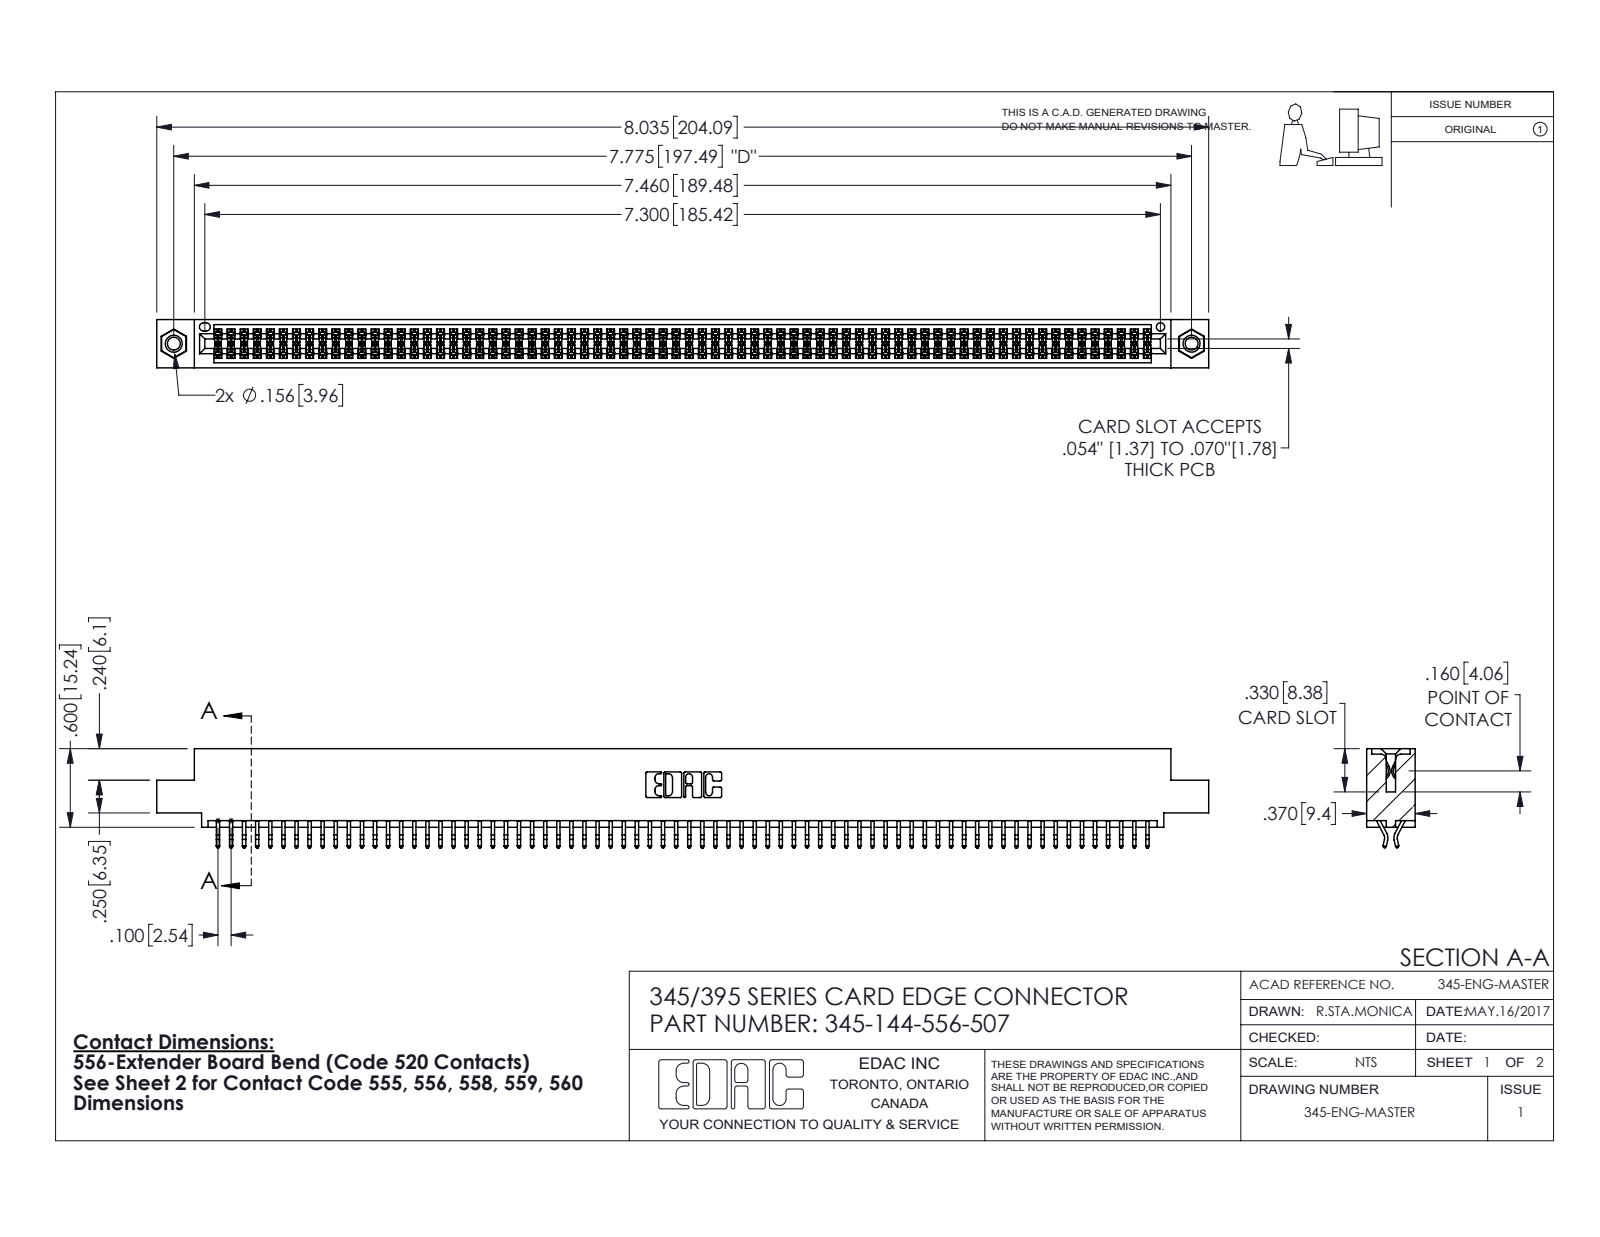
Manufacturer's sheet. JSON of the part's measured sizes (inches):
{"part_name": "345 Part_0.110 Offset - 0.156 Dia-TI; 345-292-001_556 Tail; 345-144-556-507; 345-250-001_345-250-005-103", "step_written_by": "SolidWorks 2016 (CONFIG_CONTROL_DESIGN)", "units": "inches", "bodies": {"solids": 147, "faces": 8254, "planar": 5444, "cylindrical": 2794, "other": 16}, "overall_size": [8.035, 0.757, 0.37], "volume_in3": 1.221, "surface_area_in2": 46.74, "round_holes": [[0.098, 2], [0.125, 2], [0.156, 2], [0.064, 1]], "round_bosses_or_shafts": [[0.155, 2]], "partial_cylinders_radius": [[0.006, 216], [0.01, 22], [0.007, 6], [0.031, 6], [0.026, 3], [0.01, 2], [0.014, 2], [0.019, 2]], "face_to_face_distances": [0.072, 0.298, 0.37, 0.2, 0.025, 0.098, 0.272, 0.225, 0.175, 0.149], "hole_center_spacings": [0.27, 7.539, 7.775]}
